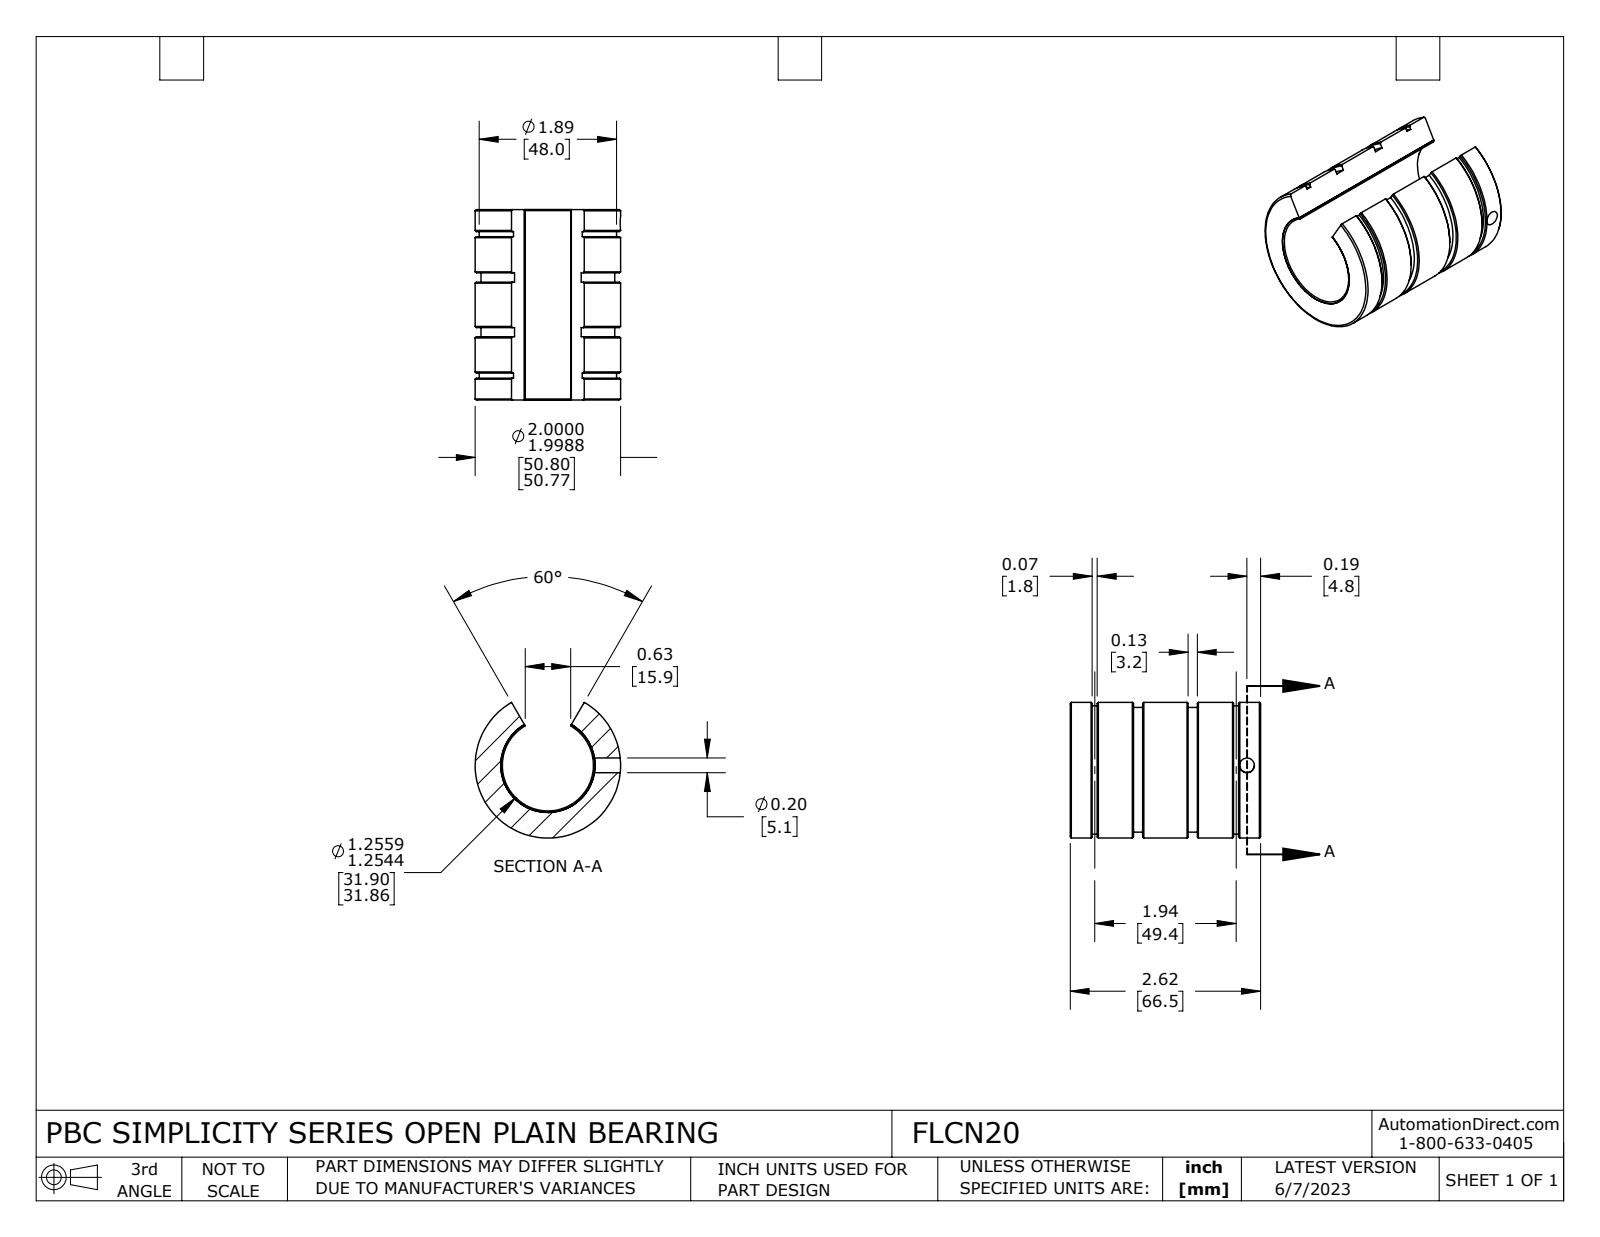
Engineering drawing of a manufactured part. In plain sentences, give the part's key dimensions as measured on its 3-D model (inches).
The part is named "FLCN20". Its 3-D file was written by "SolidWorks 2021 (CONFIG_CONTROL_DESIGN)". It is 2 solids with 82 faces: 14 planar, 40 cylindrical and 28 other. Overall it measures 2.618 by 1.999 by 1.865 inches. Its volume is 4.004 cubic inches and its surface area 47.26 square inches. Round holes: 1 of diameter 0.201, 1 of diameter 1.252, 1 of diameter 1.295. Round bosses or shafts: 1 of diameter 1.999, 1 of diameter 1.889, 1 of diameter 1.838. The main face-to-face distances are 2.617, 0.87, 1.747, 0.996, 1.621, 0.126, 0.751, 0.302, 2.316, 0.569.
